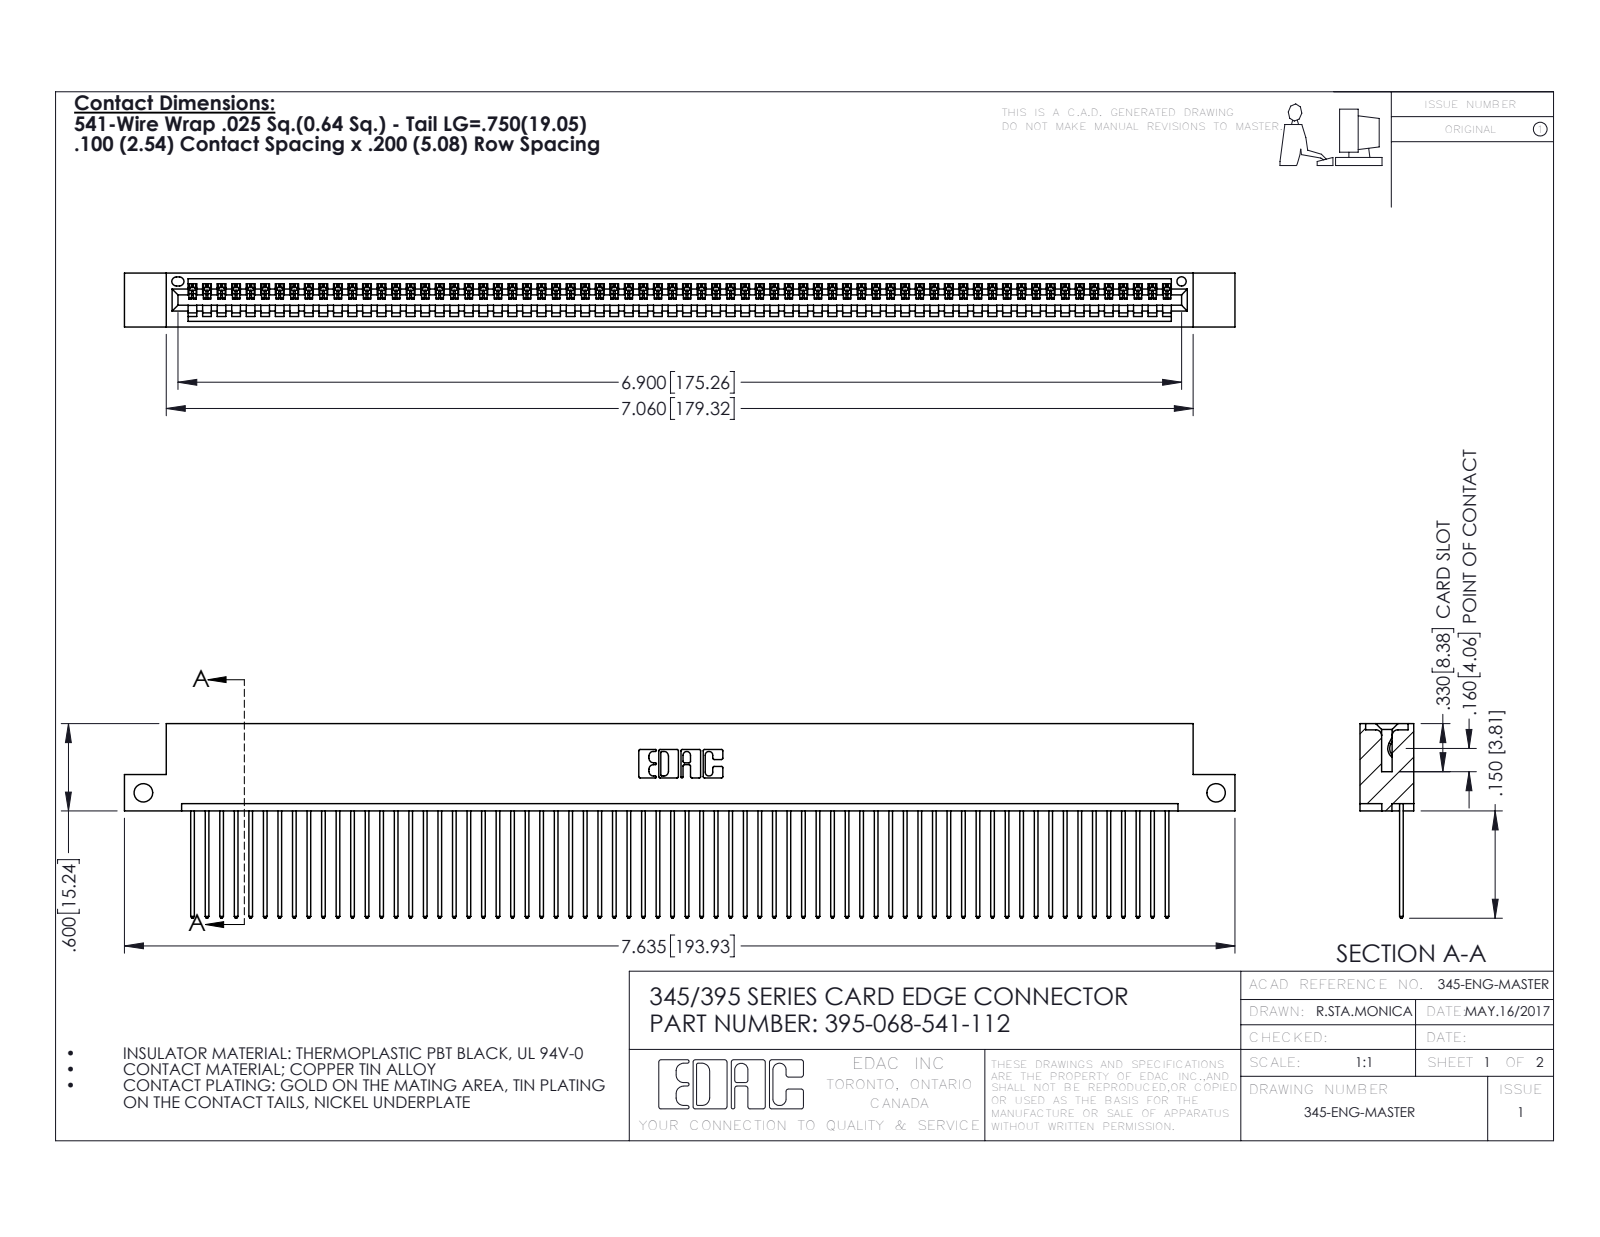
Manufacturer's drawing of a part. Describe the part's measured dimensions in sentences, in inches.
The part is named "345 Part_Flush Mounting Lugs - Side Mount; 395-068-541-112; 345-292-001_345-293-141". Its 3-D file was written by "SolidWorks 2016 (CONFIG_CONTROL_DESIGN)". It is 69 solids with 4070 faces: 2800 planar, 1270 cylindrical and 0 other. Overall it measures 7.635 by 1.337 by 0.37 inches. Its volume is 1.145 cubic inches and its surface area 41.04 square inches. Round holes: 2 of diameter 0.128, 1 of diameter 0.064. Partial cylindrical surfaces (rounded edges, fillets, slot ends): 136 of radius 0.006, 136 of radius 0.01, 22 of radius 0.01, 6 of radius 0.007, 6 of radius 0.031, 3 of radius 0.026, 2 of radius 0.031, 2 of radius 0.04. The main face-to-face distances are 0.072, 0.298, 0.098, 0.272, 0.025, 0.37, 0.2, 0.225, 0.149, 0.072. The hole center spacings are 7.375.
